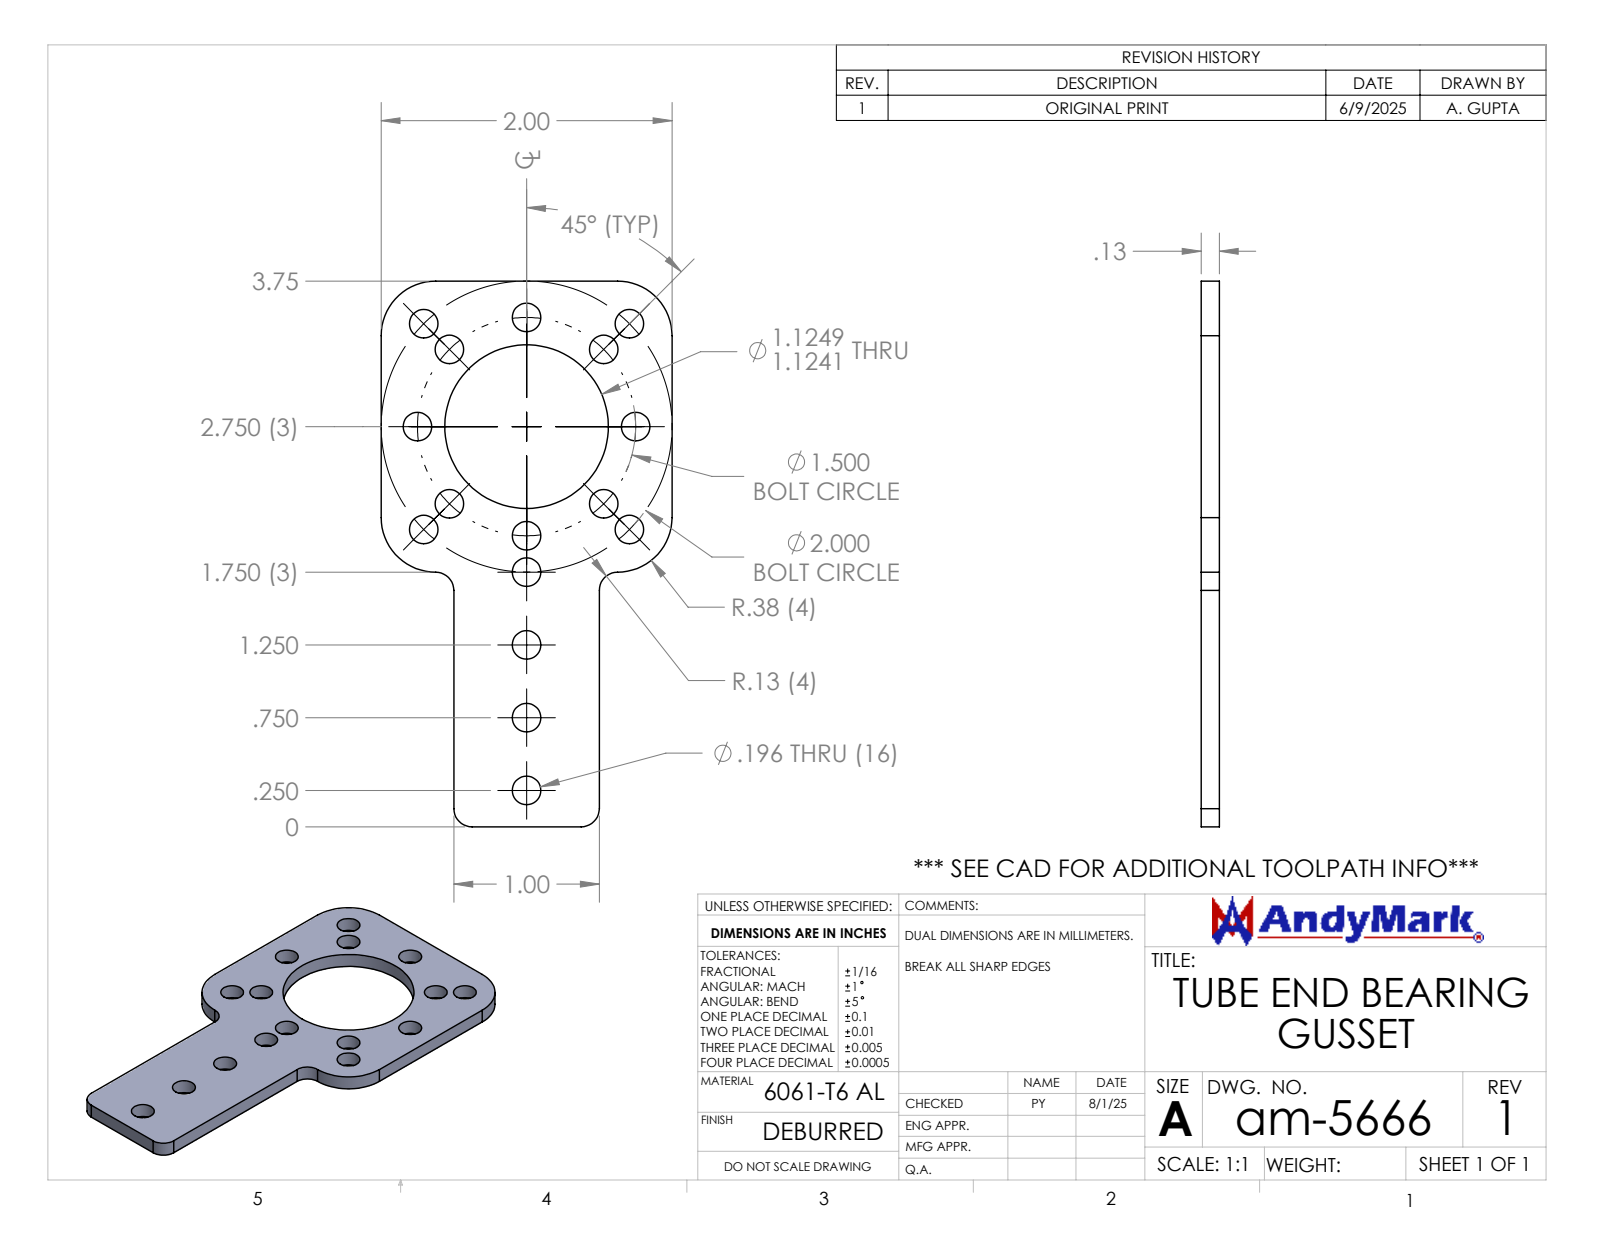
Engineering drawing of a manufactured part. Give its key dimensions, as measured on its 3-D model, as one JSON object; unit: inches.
{"part_name": "am-5666 Tube End Bearing Gusset", "step_written_by": "SolidWorks 2024 (AUTOMOTIVE_DESIGN)", "units": "inches", "bodies": {"solids": 1, "faces": 50, "planar": 8, "cylindrical": 42, "other": 0}, "overall_size": [3.75, 2, 0.125], "volume_in3": 0.519, "surface_area_in2": 11.31, "round_holes": [[0.196, 16], [1.124, 1]], "partial_cylinders_radius": [[0.125, 4], [0.375, 4]], "face_to_face_distances": [0.125, 0.5, 1.5, 1, 2, 3.75], "hole_center_spacings": [1.25, 0.708, 1.62, 0.75, 0.574, 1.061, 1.386, 1]}
